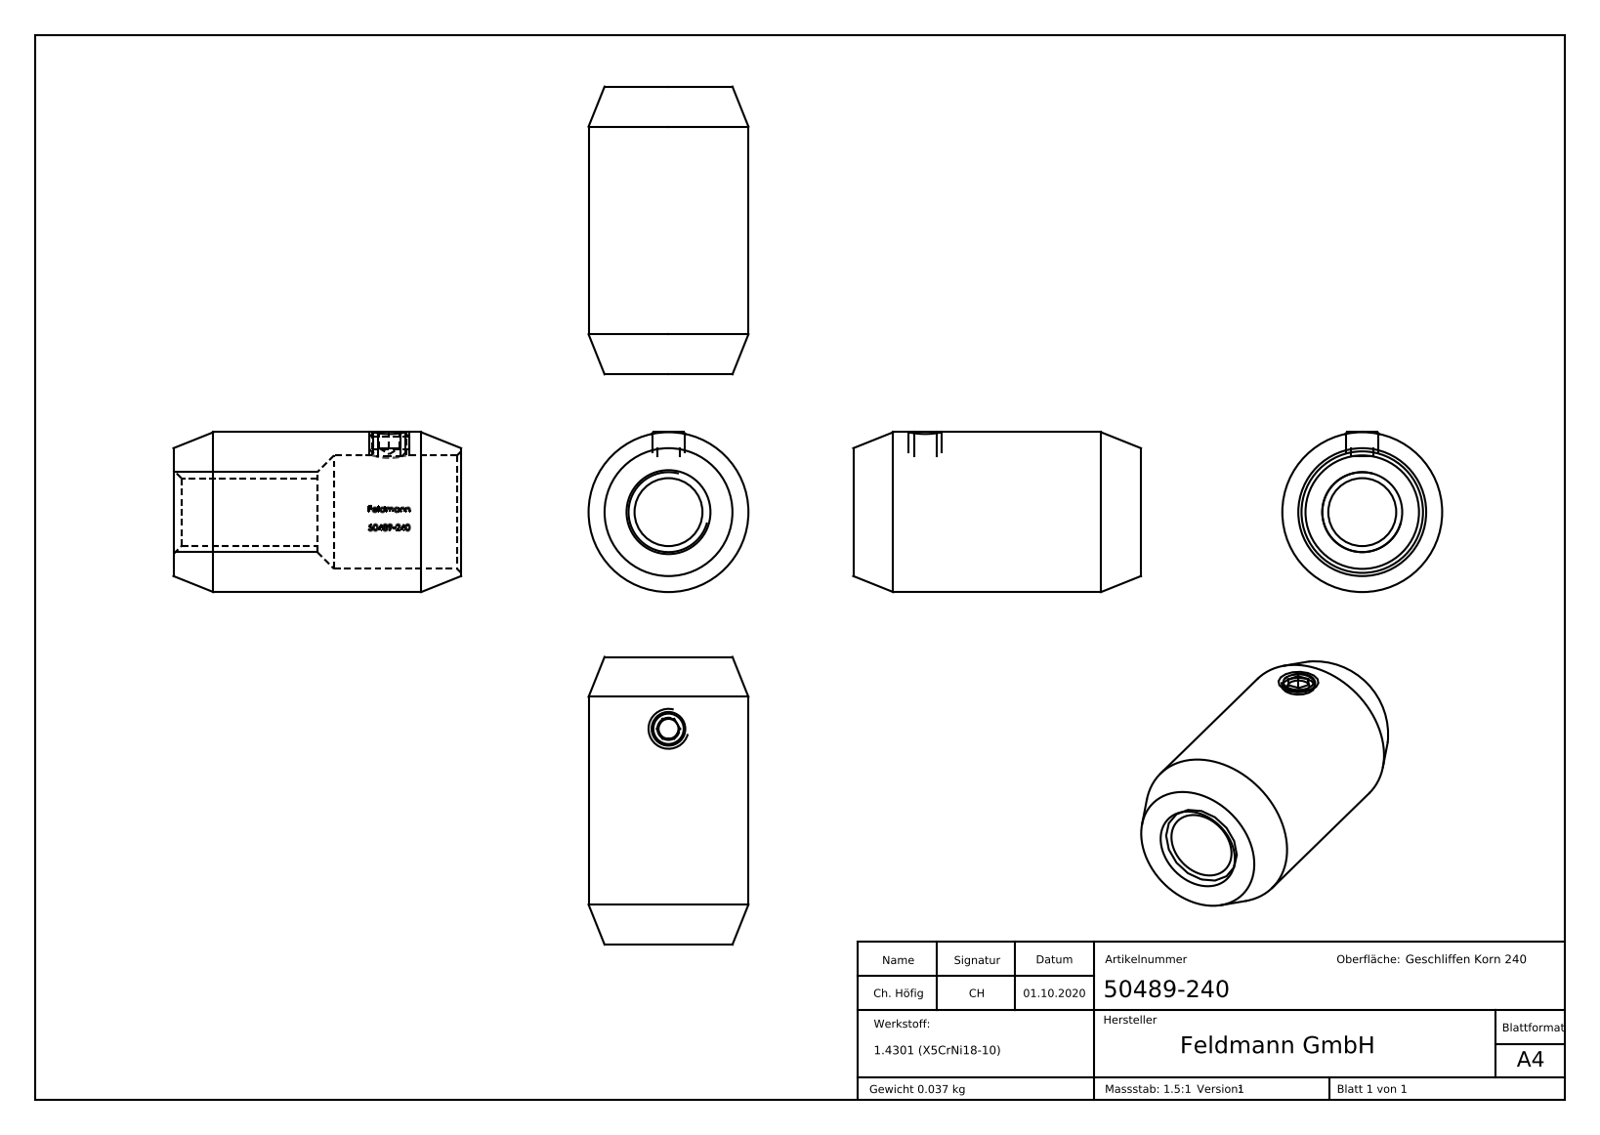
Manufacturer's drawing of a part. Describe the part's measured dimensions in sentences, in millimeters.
The part is named "DIN913; DIN913_DIN 913 M5x3; 5048X-240 Teil1; 50489-240 (+1 more)". Its 3-D file was written by "SolidWorks 2018 (CONFIG_CONTROL_DESIGN)". It is 2 solids with 275 faces: 116 planar, 37 cylindrical and 122 other. Overall it measures 70 by 36 by 20 millimeters. Its volume is 6 918 cubic millimeters and its surface area 3 833 square millimeters. Round holes: 1 of diameter 4.2, 1 of diameter 8.5, 1 of diameter 14.2. Round bosses or shafts: 1 of diameter 20, 1 of diameter 5. Partial cylindrical surfaces (rounded edges, fillets, slot ends): 1 of radius 7.2. The main face-to-face distances are 18, 36, 2.5, 3, 7.75, 10.25, 28.25, 25.75, 2, 1.
